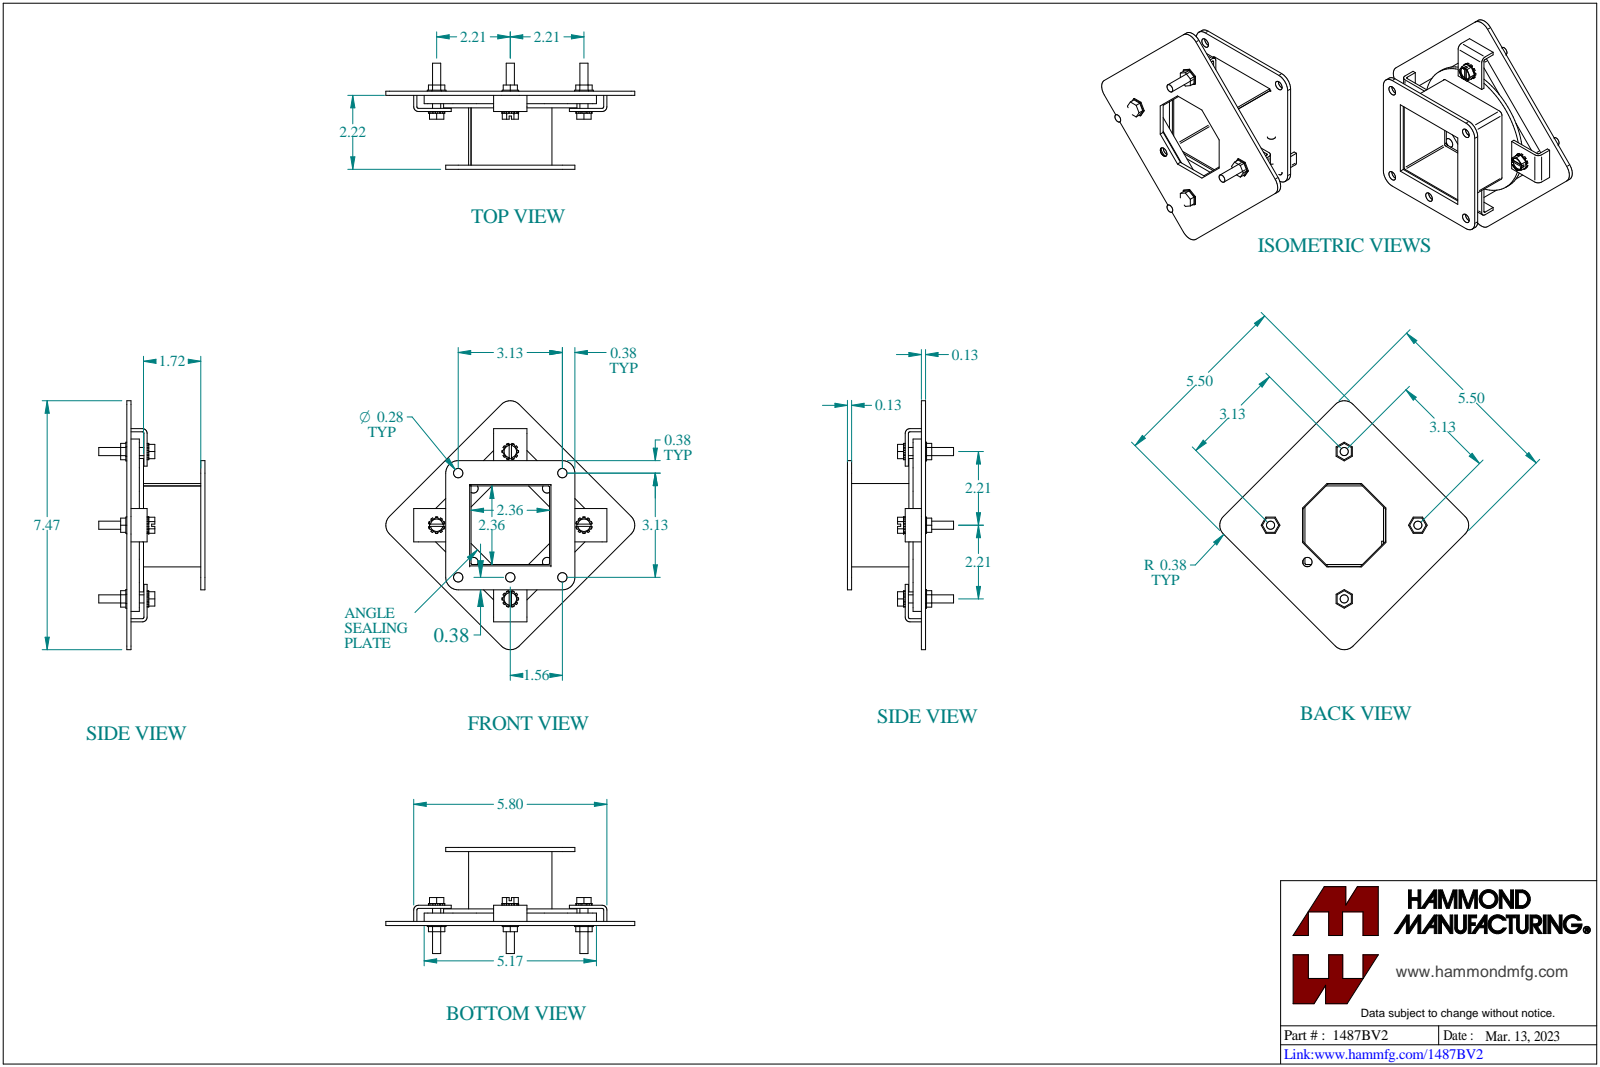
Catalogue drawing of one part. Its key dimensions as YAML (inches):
part_name: "1487BV2"
step_written_by: "SolidWorks 2023 (CONFIG_CONTROL_DESIGN)"
units: inches
bodies: {solids: 22, faces: 532, planar: 342, cylindrical: 180, other: 10}
overall_size: [7.468, 7.468, 3.309]
volume: 10.32
surface_area: 195
round_holes:
  - {diameter: 0.281, count: 16}
  - {diameter: 0.196, count: 4}
  - {diameter: 0.258, count: 4}
  - {diameter: 0.312, count: 4}
  - {diameter: 0.375, count: 2}
  - {diameter: 0.375, count: 2}
round_bosses_or_shafts:
  - {diameter: 0.244, count: 4}
  - {diameter: 4, count: 1}
partial_cylinders:
  - {radius: 0.25, count: 12}
  - {radius: 0.375, count: 12}
  - {radius: 0.048, count: 4}
  - {radius: 0.062, count: 4}
  - {radius: 0.143, count: 4}
  - {radius: 0.036, count: 3}
  - {radius: 0.108, count: 3}
face_to_face_distances: [0.125, 2.218, 0.25, 1.968, 2.093, 2.343, 2.428, 0.072, 0.125, 0.375]
hole_center_spacings: [3.494, 1.563, 2.706, 1.196, 3.125, 2.209, 4.083, 3.772]
